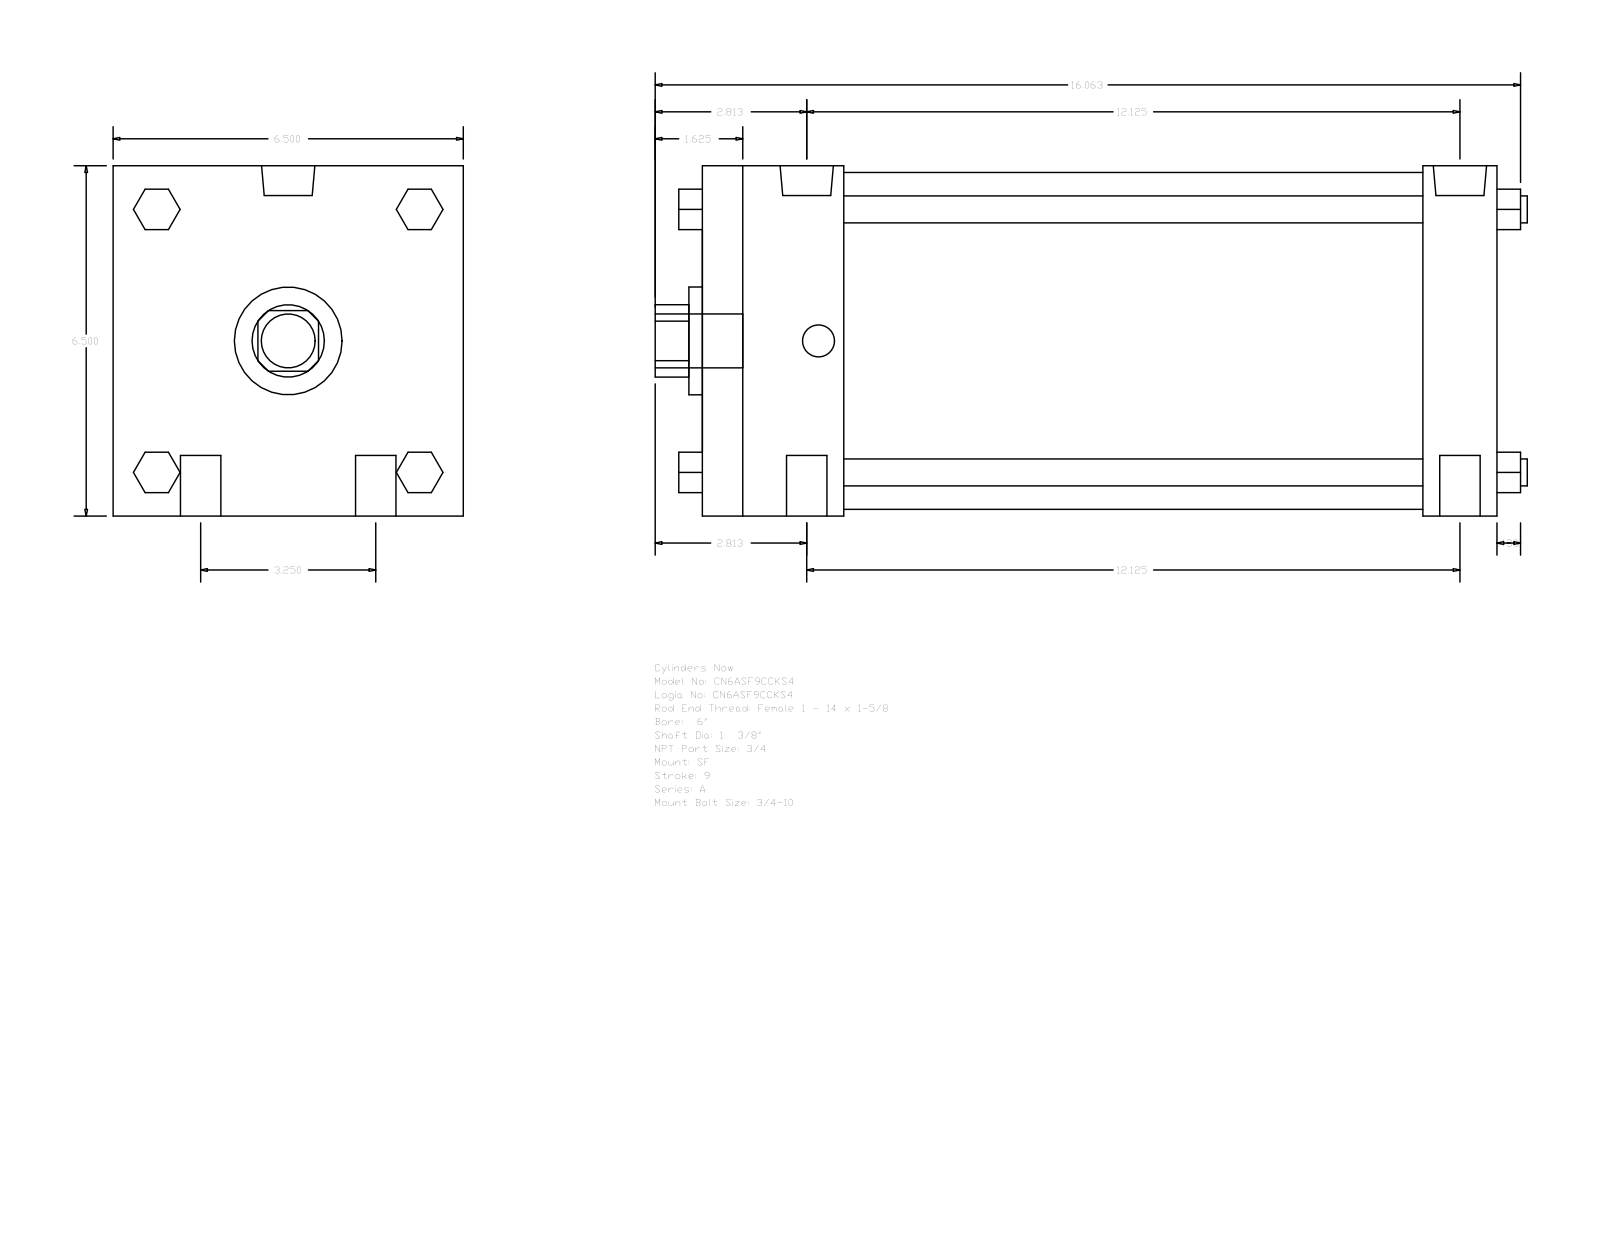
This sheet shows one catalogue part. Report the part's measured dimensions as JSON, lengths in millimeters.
{"part_name": "A_SF__0600_1.375", "step_written_by": "GSSL Pune (CONFIG_CONTROL_DESIGN)", "units": "millimeters", "bodies": {"solids": 0, "faces": 124, "planar": 94, "cylindrical": 30, "other": 0}, "overall_size": [411.16, 165.1, 165.1], "round_holes": [[34.92, 1], [50.8, 1], [158.75, 1]], "round_bosses_or_shafts": [[19.05, 4], [12.7, 4], [25.12, 2], [15.08, 2], [25.4, 1]], "partial_cylinders_radius": [[17.06, 1]], "face_to_face_distances": [165.1, 374.65, 339.72, 34.93, 66.67, 273.05, 307.98, 19.05, 61.97, 107.34]}
